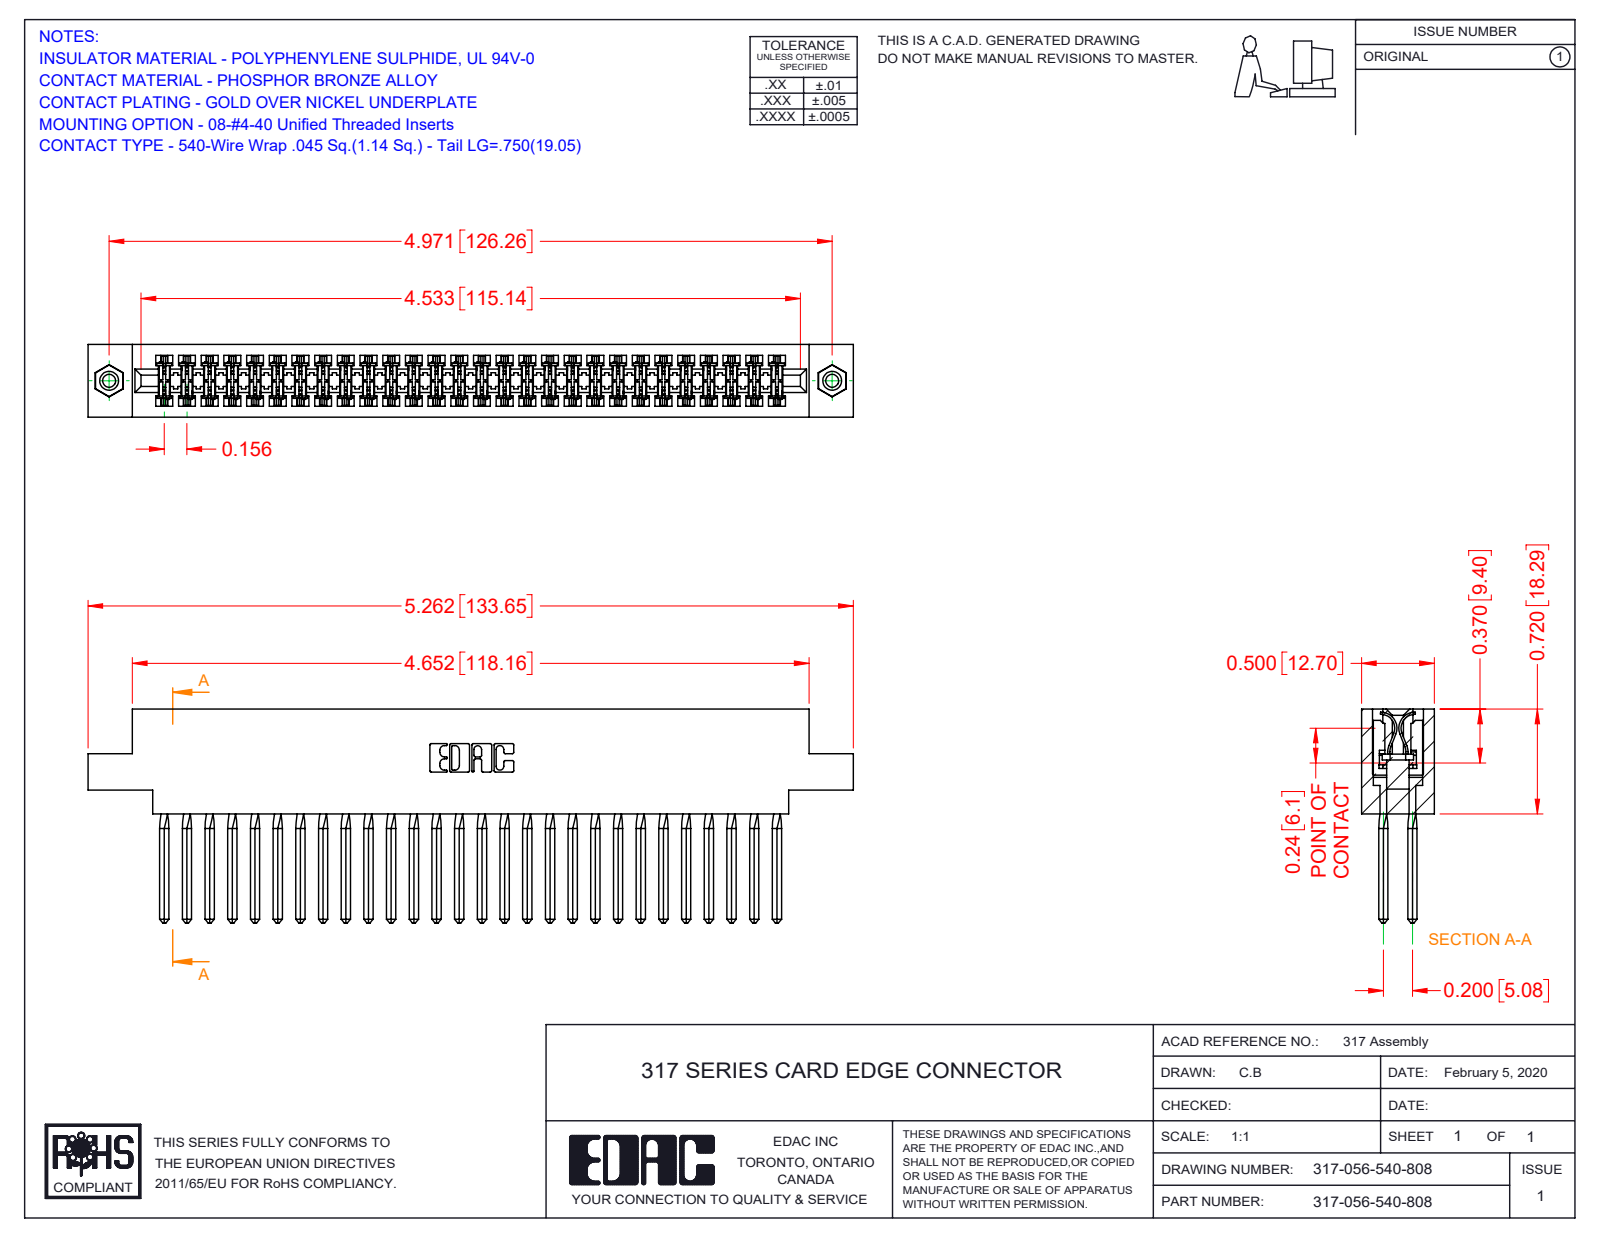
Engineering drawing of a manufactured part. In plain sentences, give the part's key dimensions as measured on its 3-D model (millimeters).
The part is named "317-056-540-878; 317 Part_.156 Dia - TI; 317-290-001_540; 345-250-001_345-250-003-102". Its 3-D file was written by "SolidWorks 2016 (CONFIG_CONTROL_DESIGN)". It is 59 solids with 5146 faces: 4178 planar, 728 cylindrical and 240 other. Overall it measures 133.7 by 37.3 by 12.7 millimeters. Its volume is 21 960 cubic millimeters and its surface area 32 220 square millimeters. Round holes: 2 of diameter 2.3, 2 of diameter 3.2, 2 of diameter 4. Round bosses or shafts: 2 of diameter 3.9. Partial cylindrical surfaces (rounded edges, fillets, slot ends): 112 of radius 0.4, 22 of radius 0.3, 6 of radius 0.2, 6 of radius 0.8, 3 of radius 0.7, 2 of radius 2.4, 2 of radius 2.5, 2 of radius 2.8. The main face-to-face distances are 12.7, 1.9, 10.8, 8.9, 2.8, 5, 2.4, 5.1, 18.3, 2.9. The hole center spacings are 126.3.
